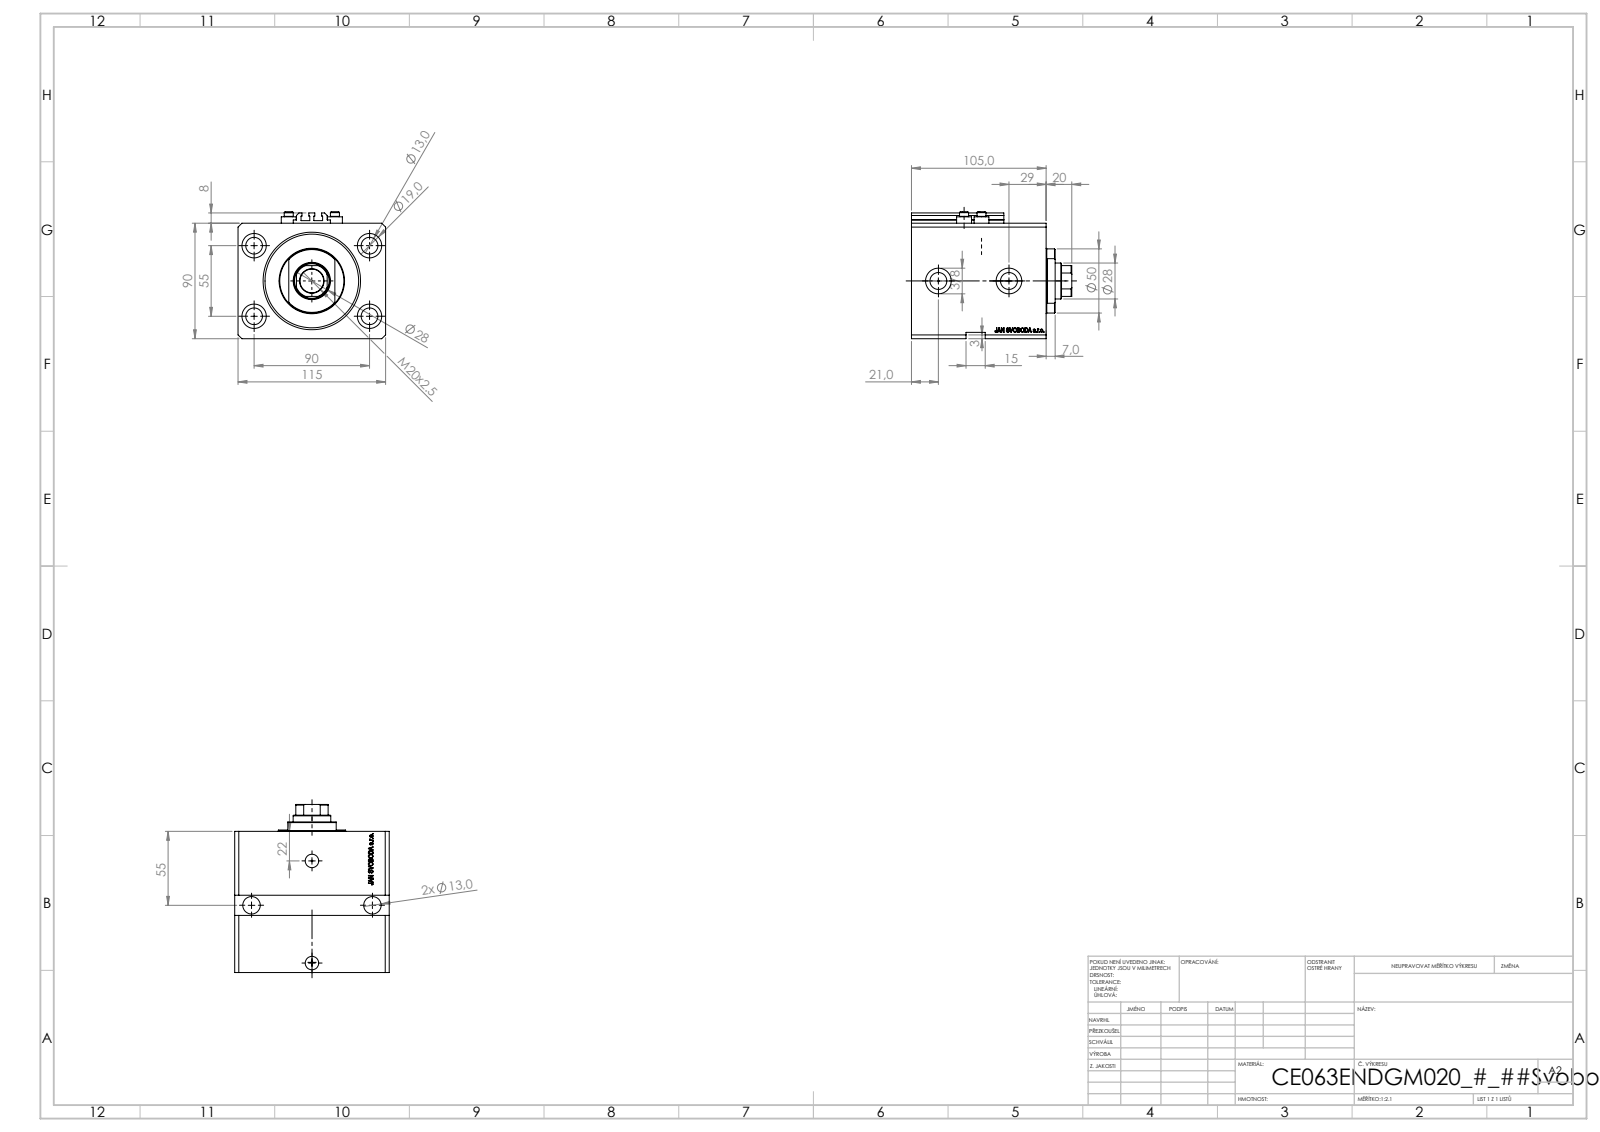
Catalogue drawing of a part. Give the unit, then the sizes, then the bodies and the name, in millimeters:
Units: millimetres
Overall size (bounding box): 125 × 115 × 99
Round holes (diameter × count): ⌀13 ×6, ⌀1.25 ×4, ⌀4 ×4, ⌀19 ×4, ⌀10 ×2, ⌀13.16 ×2, ⌀20 ×2, ⌀18.5 ×1, ⌀28 ×1, ⌀63 ×1, ⌀76 ×1
Round bosses / shafts (diameter × count): ⌀11.6 ×4, ⌀7 ×4, ⌀50 ×1
Partial cylindrical surfaces — rounded edges, fillets, slot ends (radius × count): R0.2 ×10, R13.5 ×1
Main face-to-face distances: 90, 20, 115, 85, 105, 87.1, 17.9, 67.1, 40, 65
Hole centre spacings: 52.74, 55, 90, 13.6, 27.39, 28.46, 33.62, 36
Volume: 950 937 mm³ · Surface area: 155 133 mm²
Bodies: 8 solids, 1123 faces (547 planar, 138 cylindrical, 438 other)
Part name (STEP PRODUCT): V250CE_E_Body; V250CE_VC_E; V250CE_C_VCP; ALLEN BOLT V250CE
STEP written by: SolidWorks 2019 (CONFIG_CONTROL_DESIGN)
